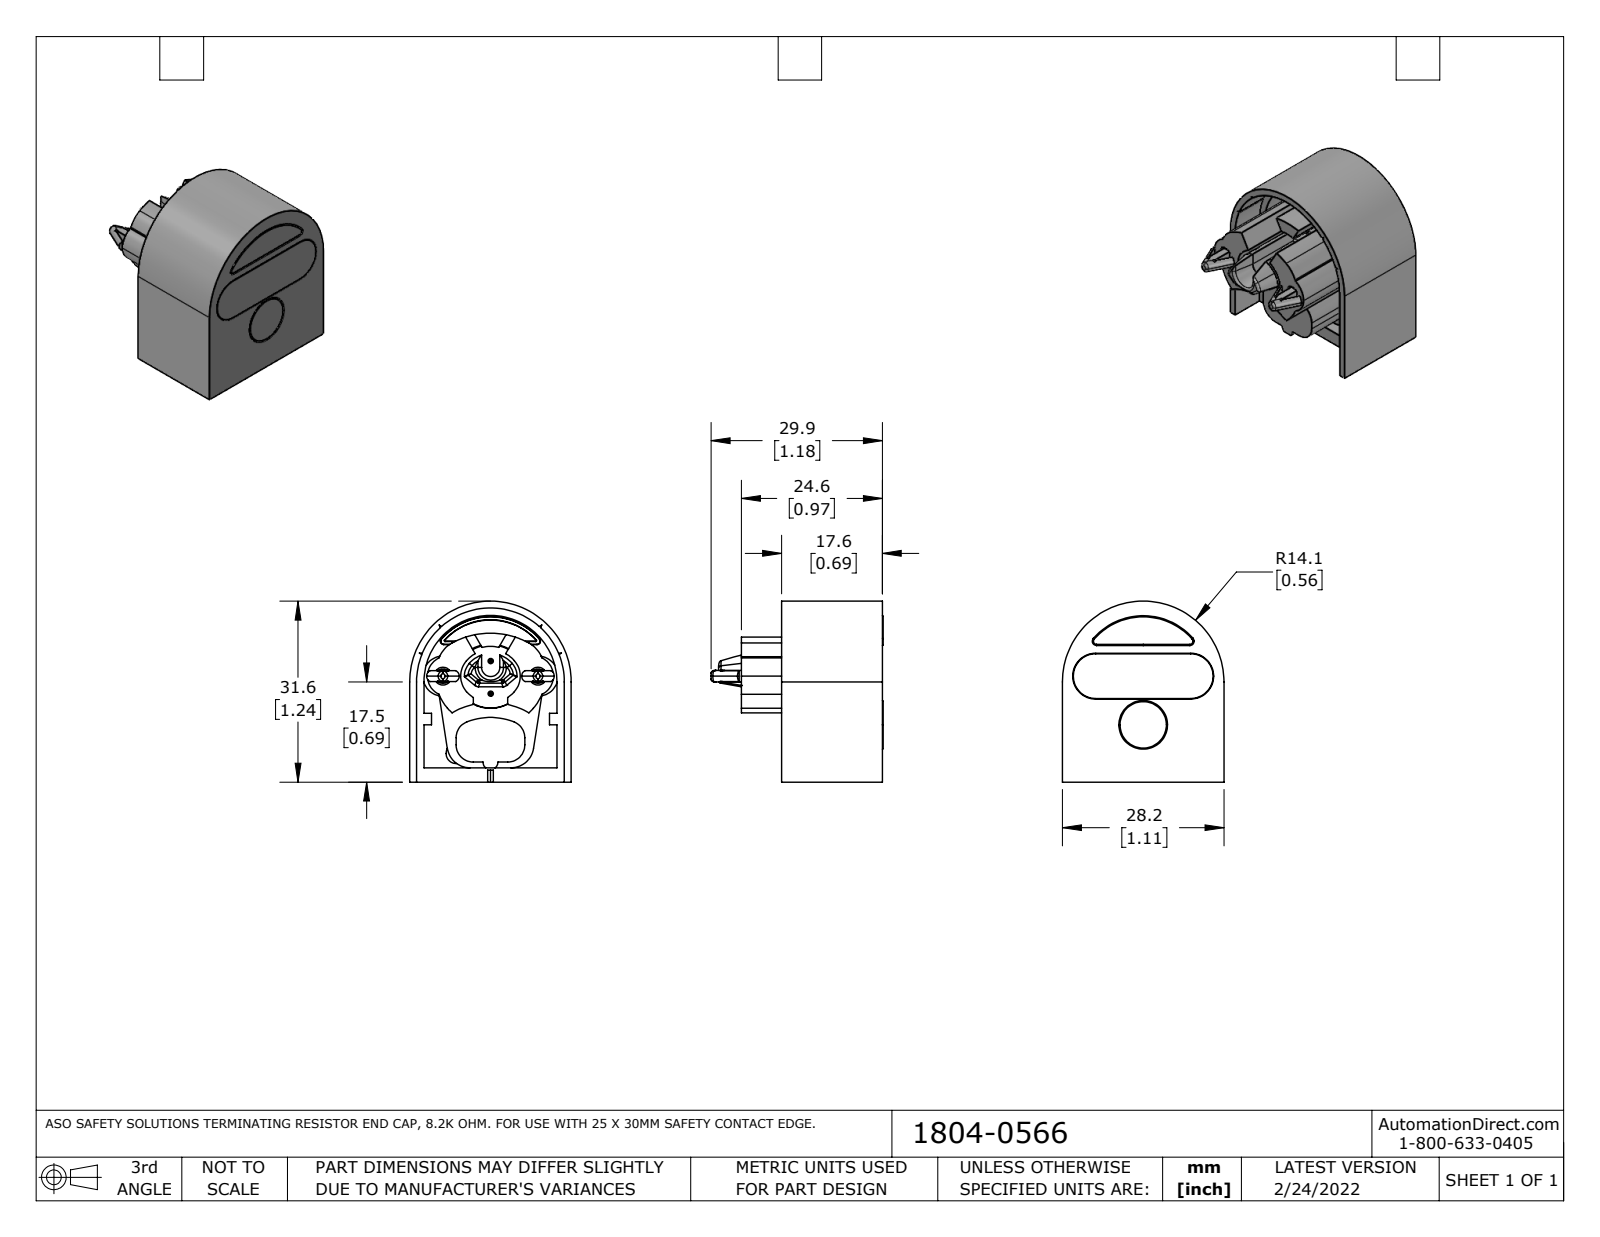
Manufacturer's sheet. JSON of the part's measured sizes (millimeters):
{"part_name": "1804-0566_Default", "step_written_by": "SolidWorks 2021 (CONFIG_CONTROL_DESIGN)", "units": "millimeters", "bodies": {"solids": 6, "faces": 471, "planar": 167, "cylindrical": 204, "other": 100}, "overall_size": [31.6, 30, 28.2], "volume_mm3": 9650, "surface_area_mm2": 10490, "round_holes": [[0.5, 4], [3.5, 3], [0.7, 2], [3.1, 2], [4, 2], [5.5, 2], [0.8, 1]], "round_bosses_or_shafts": [[5, 2], [3.5, 2], [2.5, 2], [2, 2], [1.7, 2], [0.9, 2], [0.6, 2]], "partial_cylinders_radius": [[1, 12], [0.1, 9], [0.3, 6], [3, 6], [3.5, 6], [0.5, 5], [4, 4], [5, 4]], "face_to_face_distances": [2.5, 1.8, 1, 28.2, 0.8, 1.3, 2, 25.7, 1.2, 27], "hole_center_spacings": [1.4, 16.6, 23.5, 24, 5.7, 8.7, 8.8, 8.8]}
